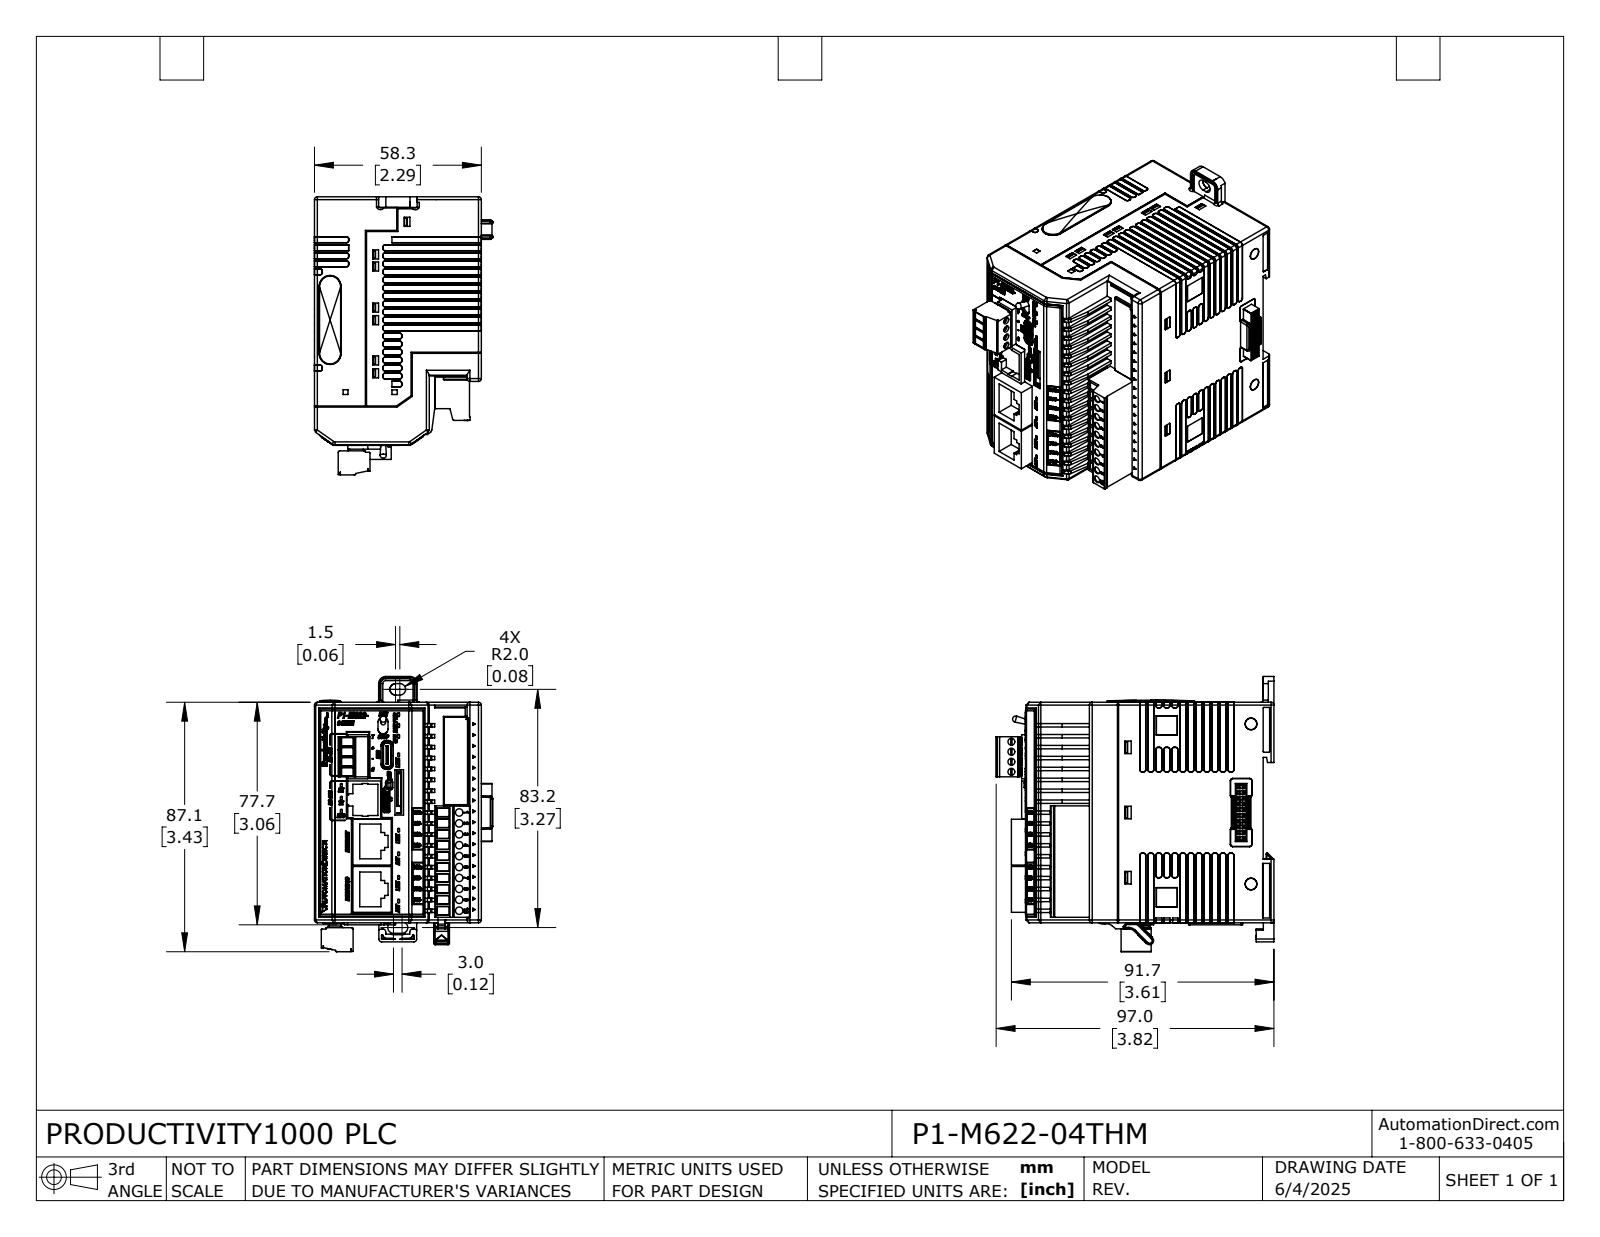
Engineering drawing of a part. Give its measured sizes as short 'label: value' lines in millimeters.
name: P1-M622-04THM
written by: SolidWorks 2024 (AUTOMOTIVE_DESIGN)
unit: mm
bodies: 15 solids, 3820 faces (2211 planar, 892 cylindrical, 717 other)
size: 93.6 × 91.7 × 62.3
volume: 35 840 mm³; area: 77 550 mm²
rounds: 186× R0.3, 80× R0.2, 53× R0.5, 33× R1, 8× R2, 7× R0.6, 7× R1.5, 4× R0.3
face distances: 1.3, 0.5, 56.8, 1, 57.8, 76.5, 76.8, 58.3, 76.7, 77
